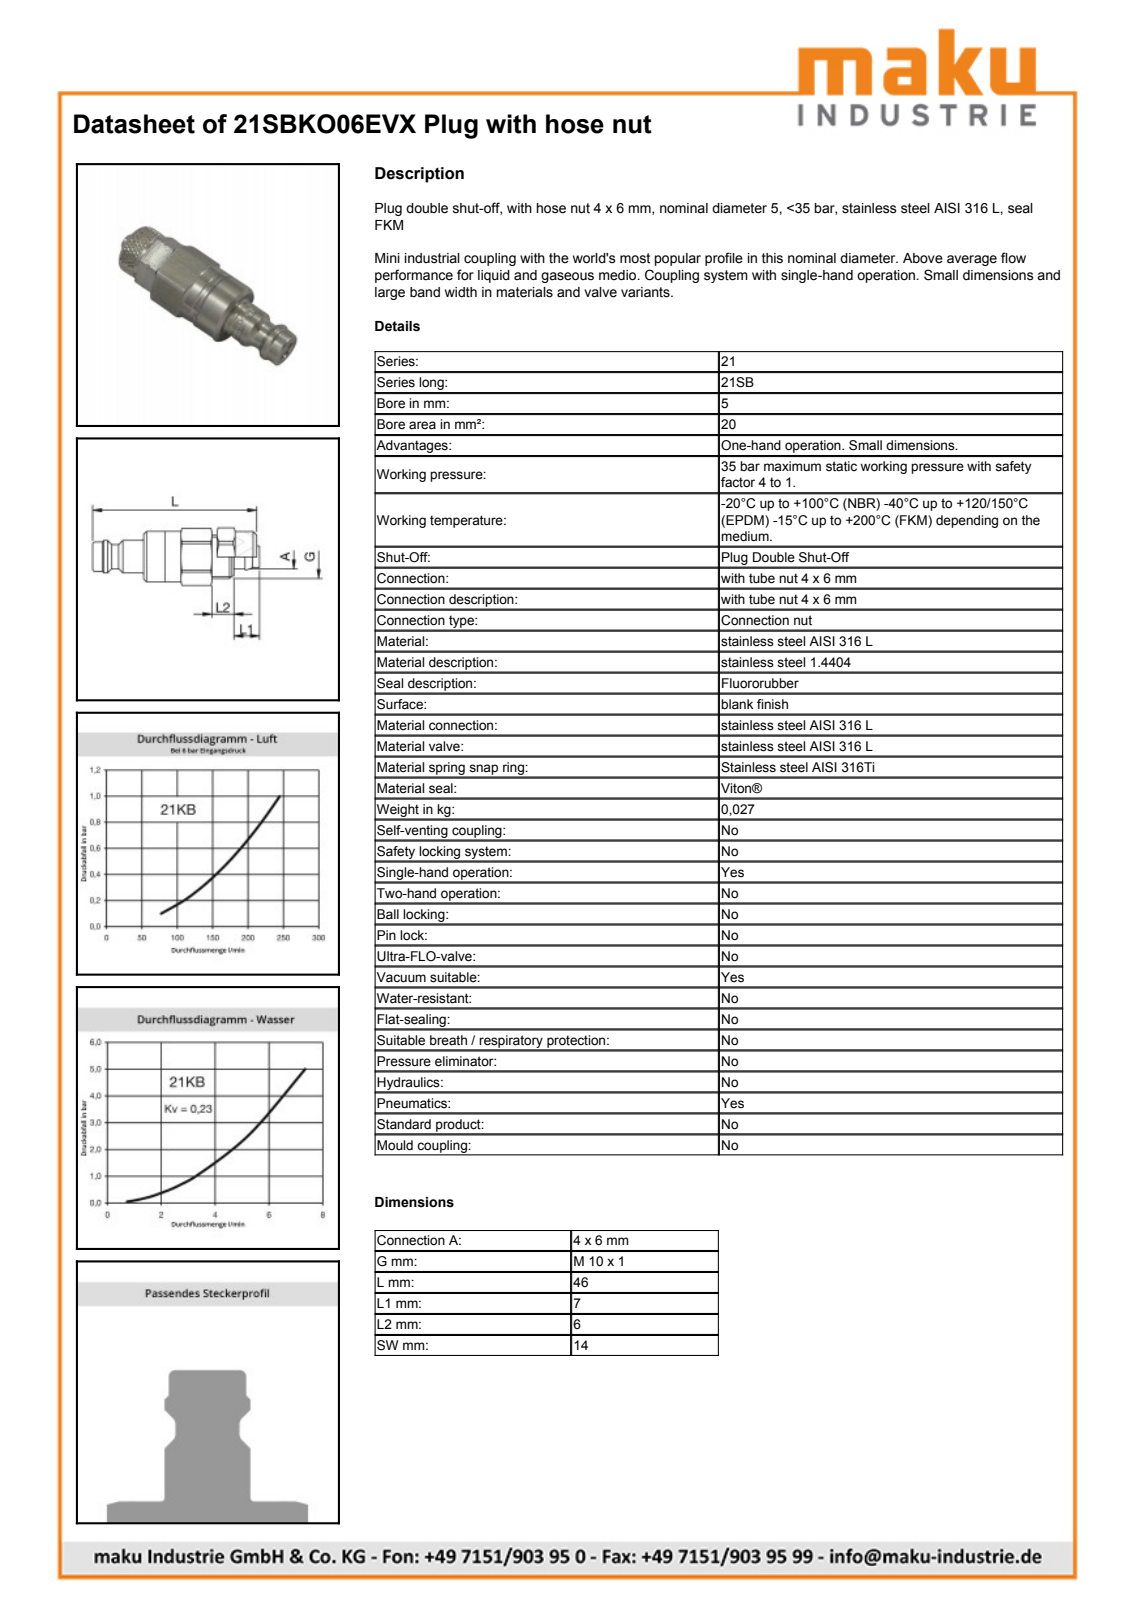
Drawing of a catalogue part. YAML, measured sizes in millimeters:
part_name: "D105926"
step_written_by: "Autodesk Inventor 2011 (AUTOMOTIVE_DESIGN)"
units: millimeters
bodies: {solids: 1, faces: 101, planar: 23, cylindrical: 29, other: 49}
overall_size: [45.85, 15.49, 15.34]
volume: 4775
surface_area: 2804
round_holes:
  - {diameter: 6.2, count: 1}
  - {diameter: 10, count: 1}
  - {diameter: 10.5, count: 1}
  - {diameter: 12, count: 1}
round_bosses_or_shafts:
  - {diameter: 14, count: 1}
  - {diameter: 10.95, count: 1}
  - {diameter: 9, count: 1}
  - {diameter: 8.4, count: 1}
  - {diameter: 8.1, count: 1}
  - {diameter: 6.7, count: 1}
  - {diameter: 4.6, count: 1}
  - {diameter: 4, count: 1}
partial_cylinders:
  - {radius: 6.7, count: 1}
  - {radius: 7.9, count: 1}
face_to_face_distances: [14, 12, 5, 12.1, 6.1, 6, 13.85, 18.65, 24.75, 30.75]
